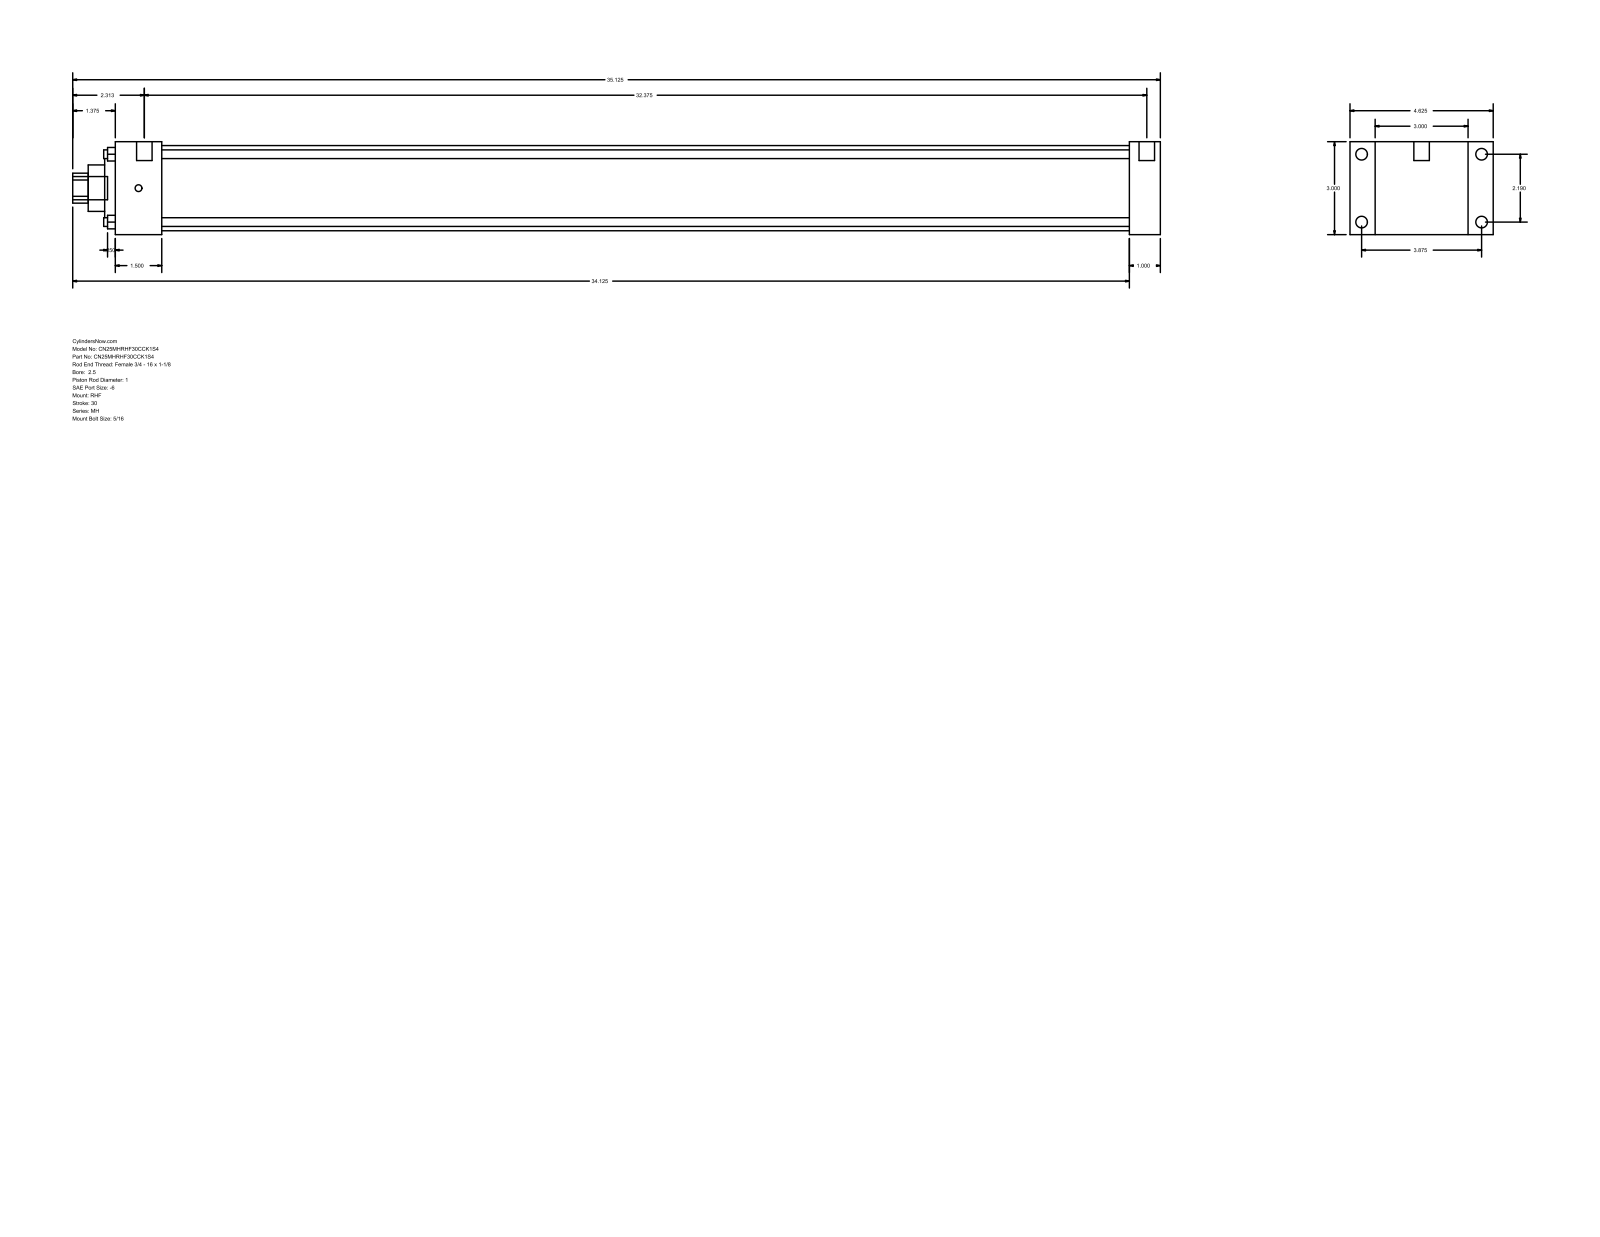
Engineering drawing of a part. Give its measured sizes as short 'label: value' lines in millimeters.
name: MH_RHF__0250_1
written by: GSSL Pune (CONFIG_CONTROL_DESIGN)
unit: mm
bodies: 0 solids, 90 faces (61 planar, 29 cylindrical, 0 other)
size: 892.17 × 117.47 × 76.2
holes: 4× ⌀7.14, 1× ⌀25.4, 1× ⌀38.1, 1× ⌀60.33, 1× ⌀69.85
bosses: 4× ⌀9.53, 4× ⌀5.56, 2× ⌀12.7, 1× ⌀19.05
rounds: 1× R12.29
face distances: 76.2, 25.4, 20.64, 96.84, 831.85, 857.25, 117.48, 38.11, 793.74, 819.14
hole spacings: 39.33, 55.62, 78.66
